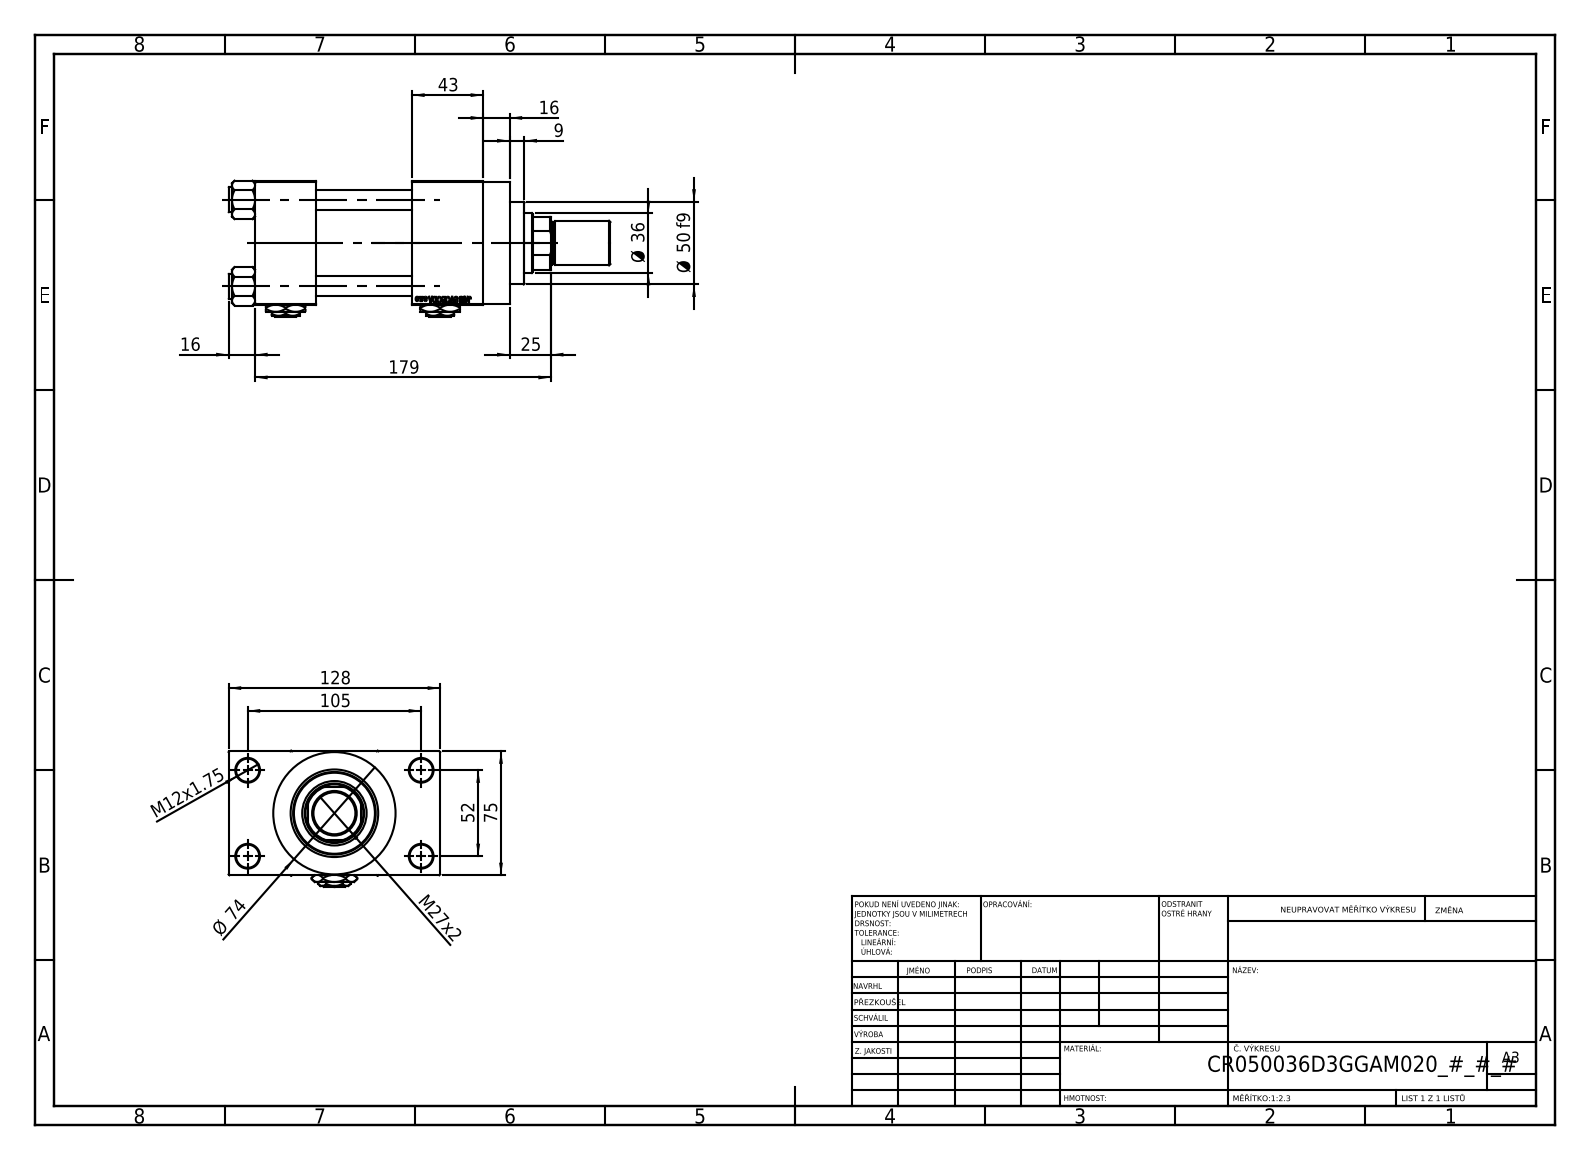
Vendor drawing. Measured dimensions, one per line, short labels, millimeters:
name: V215CR_D_TYCINKA; V215CR_D_Body; V215_VC_A; V215CR_VCP_D (+3 more)
written by: SolidWorks 2019 (CONFIG_CONTROL_DESIGN)
unit: mm
bodies: 14 solids, 1219 faces (549 planar, 104 cylindrical, 566 other)
size: 231 × 128 × 82.27
volume: 842 388 mm³; area: 182 295 mm²
holes: 4× ⌀12, 4× ⌀14, 2× ⌀7, 2× ⌀20.96, 2× ⌀30, 1× ⌀25.5, 1× ⌀36, 1× ⌀39, 1× ⌀41, 1× ⌀53
bosses: 4× ⌀15, 1× ⌀74, 1× ⌀56, 1× ⌀50, 1× ⌀27, 1× ⌀25
rounds: 1× R17.5
face distances: 75, 58, 37, 95, 101.5, 26.5, 138, 43, 101, 16
hole spacings: 26.35, 36.98, 52.3, 58.43, 58.59, 78.65, 94.37, 52
